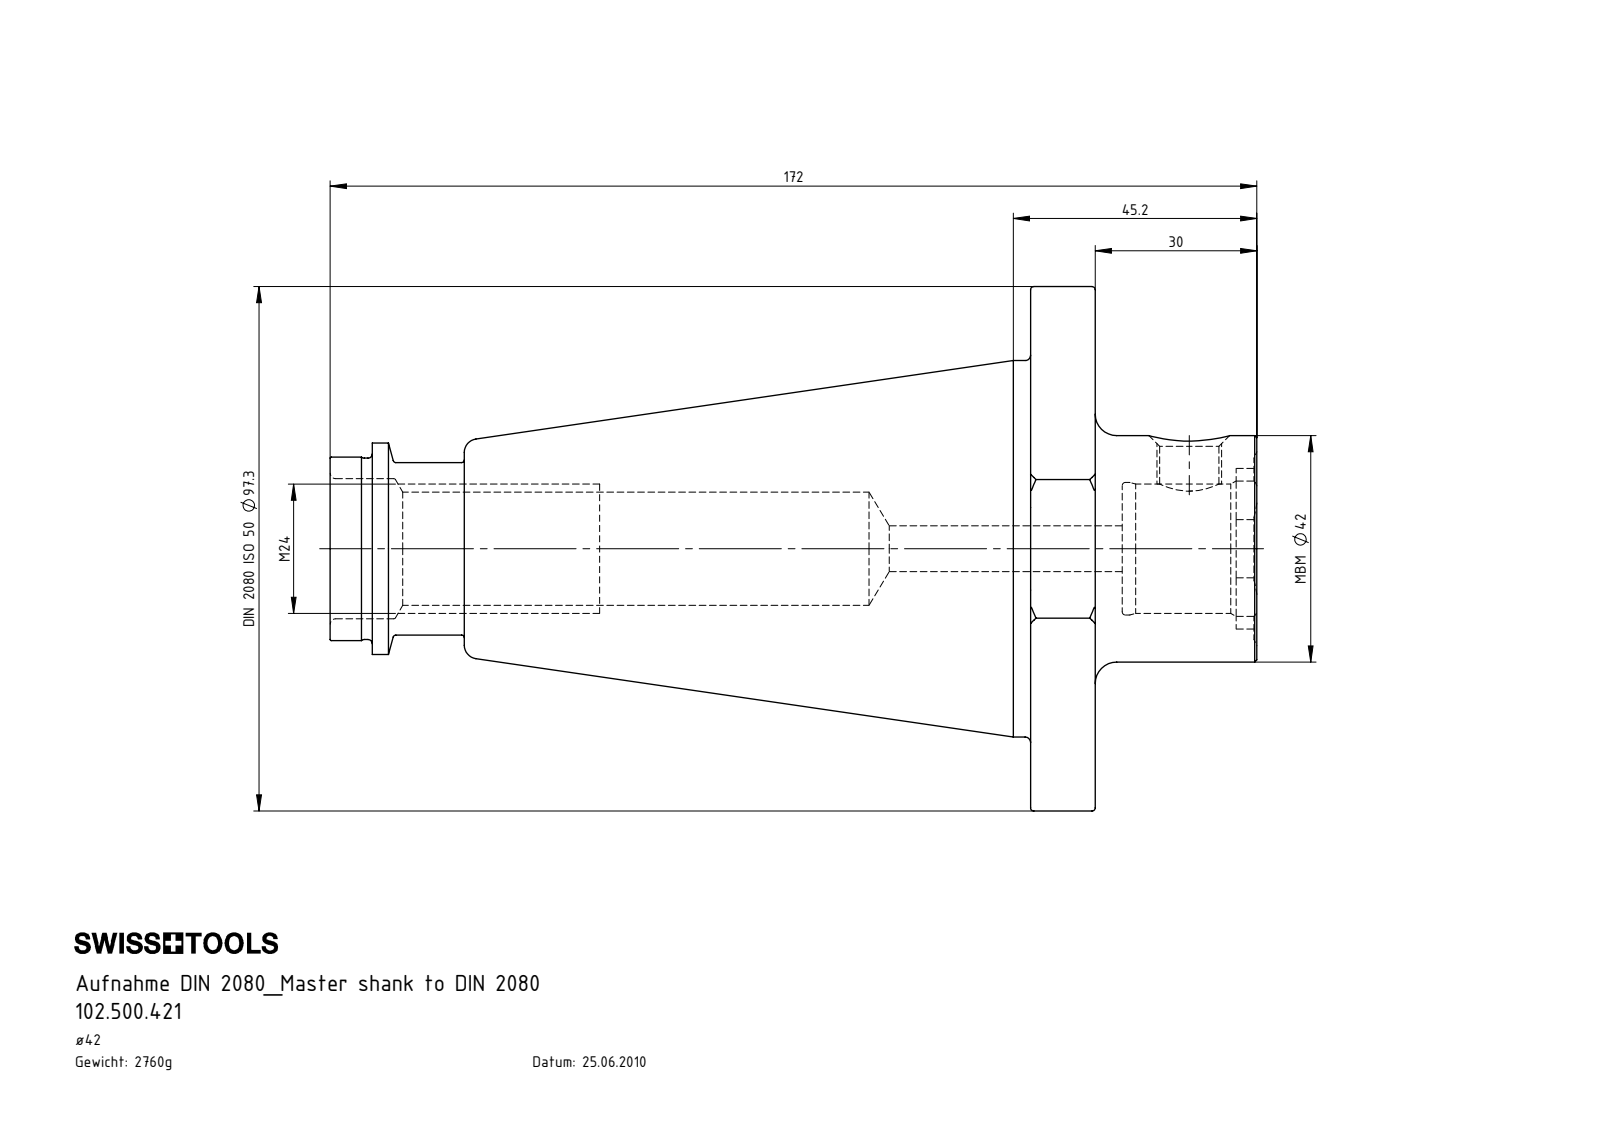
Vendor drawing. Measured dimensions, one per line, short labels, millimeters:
name: 102.500.421
written by: SolidWorks 2017 (CONFIG_CONTROL_DESIGN)
unit: mm
bodies: 1 solid, 131 faces (33 planar, 49 cylindrical, 49 other)
size: 172 × 97.3 × 93.84
volume: 351 586 mm³; area: 50 134 mm²
holes: 1× ⌀8.5, 1× ⌀11, 1× ⌀21, 1× ⌀24, 1× ⌀24.6, 1× ⌀26
bosses: 1× ⌀97.3, 1× ⌀69.85, 1× ⌀42, 1× ⌀39.24, 1× ⌀34.05, 1× ⌀33.65, 1× ⌀32
rounds: 12× R2, 4× R5.2, 1× R14.9, 1× R16.52
face distances: 12, 17, 5, 38.15, 26.15, 21.15, 42, 30, 25, 3.85
